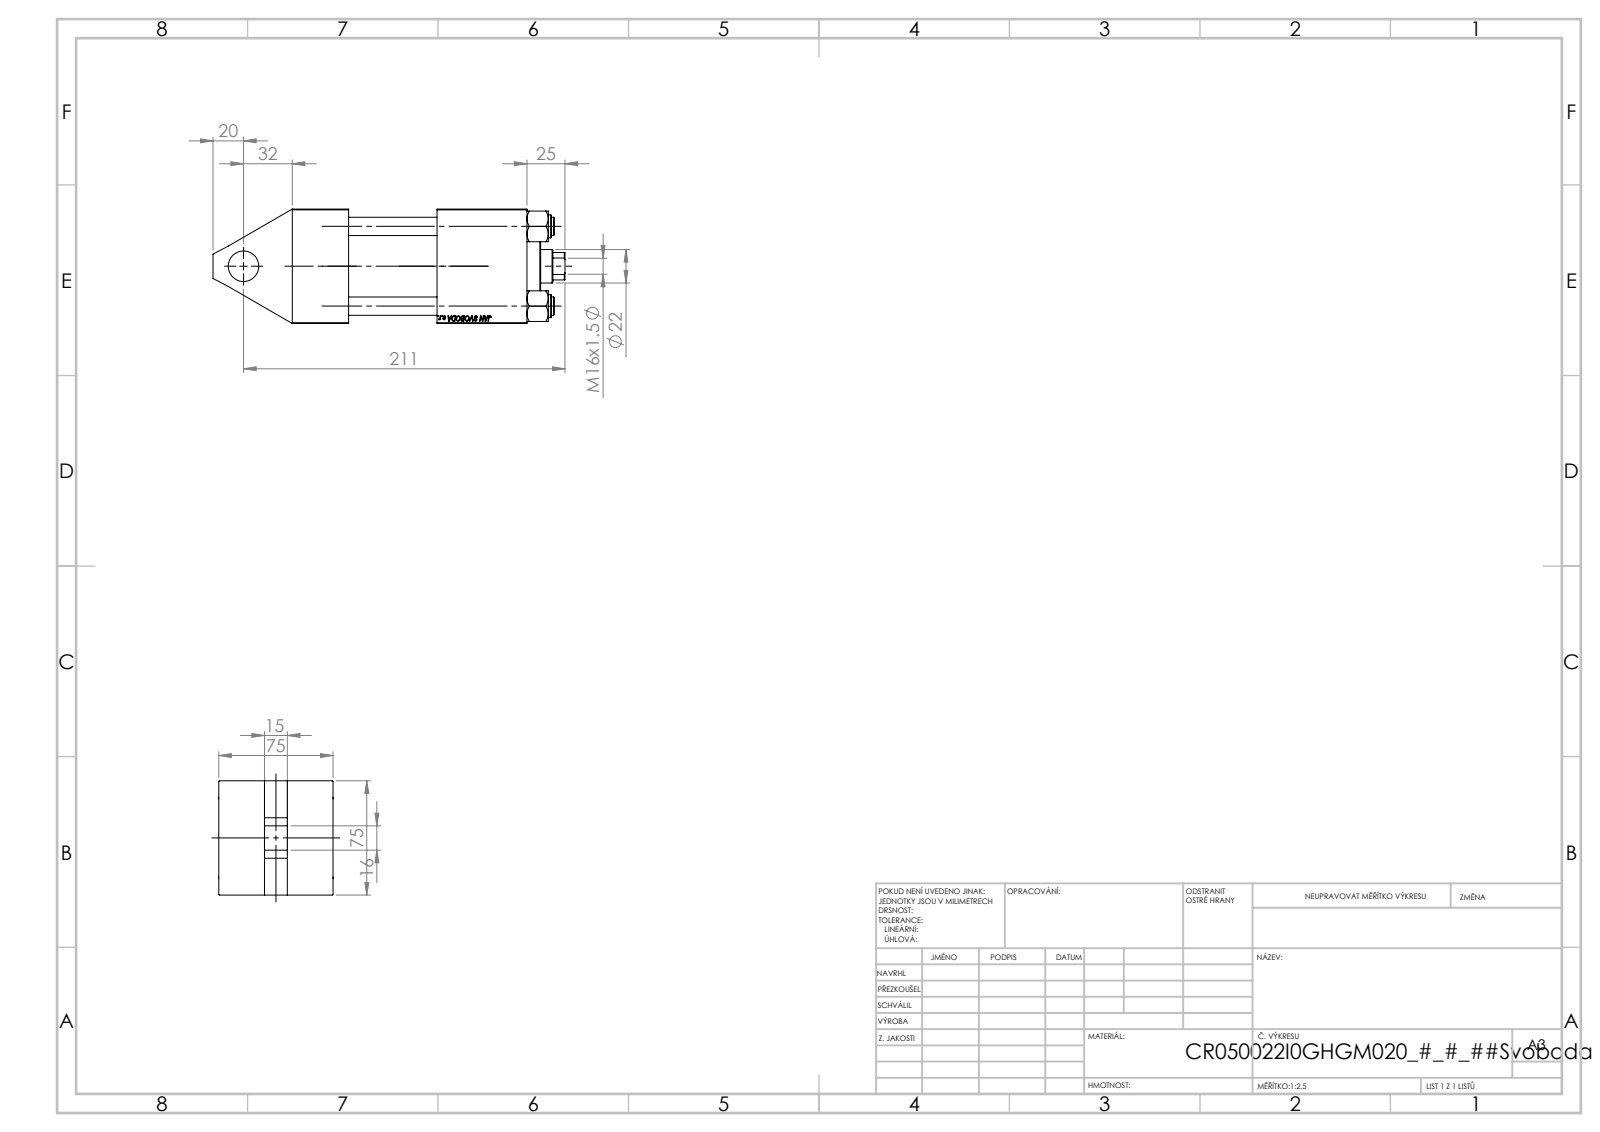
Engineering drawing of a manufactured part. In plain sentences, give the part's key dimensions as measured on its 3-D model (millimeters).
The part is named "V215CR_VCP_I; V215_VC_A; NUT_M5_I; V215CR_I_Body (+1 more)". Its 3-D file was written by "SolidWorks 2019 (CONFIG_CONTROL_DESIGN)". It is 11 solids with 1079 faces: 502 planar, 81 cylindrical and 496 other. Overall it measures 231 by 75.54 by 75 millimeters. Its volume is 699 574 cubic millimeters and its surface area 156 292 square millimeters. Round holes: 4 of diameter 12, 2 of diameter 7, 2 of diameter 20.96, 2 of diameter 30, 1 of diameter 10.5, 1 of diameter 20, 1 of diameter 22, 1 of diameter 25, 1 of diameter 41, 1 of diameter 50, 1 of diameter 53. Round bosses or shafts: 4 of diameter 15, 1 of diameter 56, 1 of diameter 34. Partial cylindrical surfaces (rounded edges, fillets, slot ends): 1 of radius 10.5. The main face-to-face distances are 75, 117, 37, 154, 45, 30, 95, 58, 59, 125.3. The hole center spacings are 36.98, 52.3, 73.96, 50.5, 93.5, 144.
